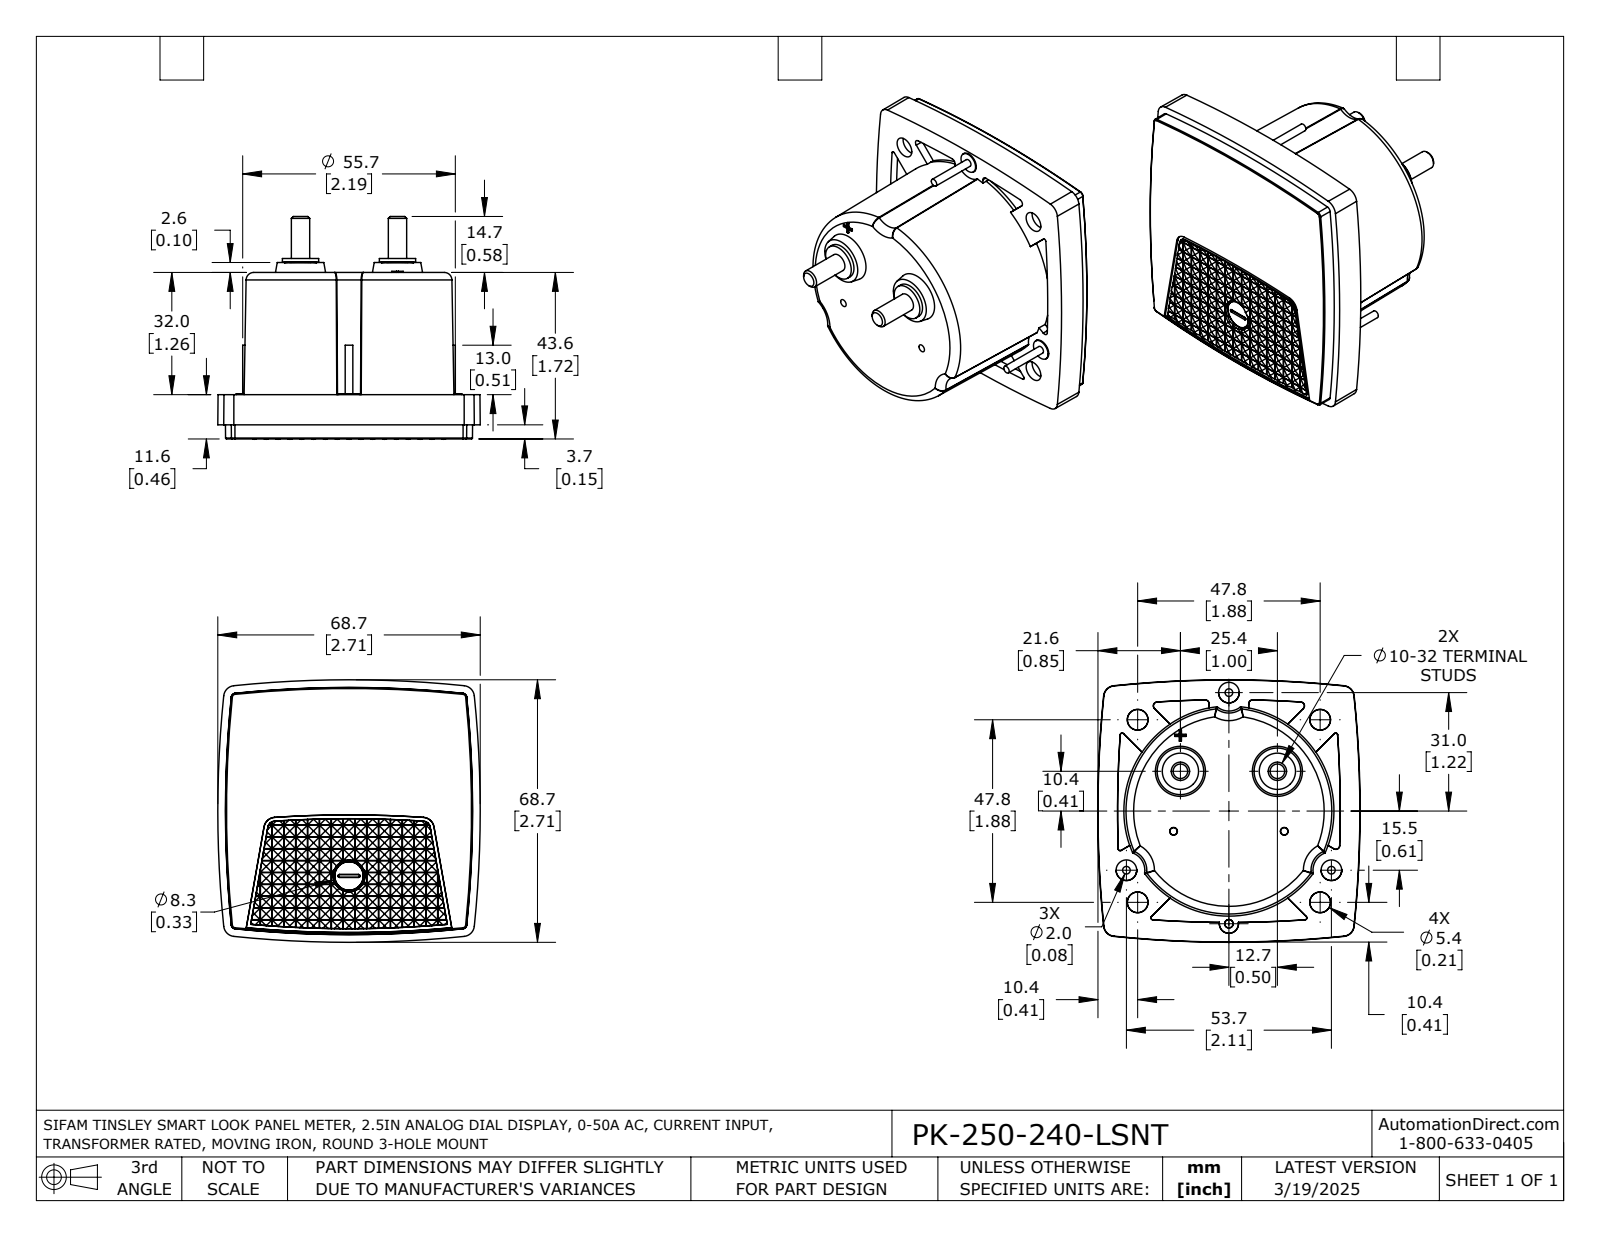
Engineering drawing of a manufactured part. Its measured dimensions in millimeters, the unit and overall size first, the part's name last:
Units: millimetres
Overall size (bounding box): 68.7 × 68.7 × 58.3
Round bosses / shafts (diameter × count): ⌀5.4 ×3, ⌀2 ×3, ⌀9.5 ×2, ⌀4.8 ×2, ⌀5.5 ×1
Partial cylindrical surfaces — rounded edges, fillets, slot ends (radius × count): R4.2 ×2, R27.5 ×1
Main face-to-face distances: 43.6, 32, 11.6, 0.6, 2.2, 2.4, 7.9, 3, 1.8, 34.2
Volume: 124 400 mm³ · Surface area: 19 620 mm²
Bodies: 1 solid, 1550 faces (1165 planar, 265 cylindrical, 120 other)
Part name (STEP PRODUCT): PK-250-240-LSNT
STEP written by: SolidWorks 2021 (AUTOMOTIVE_DESIGN)
